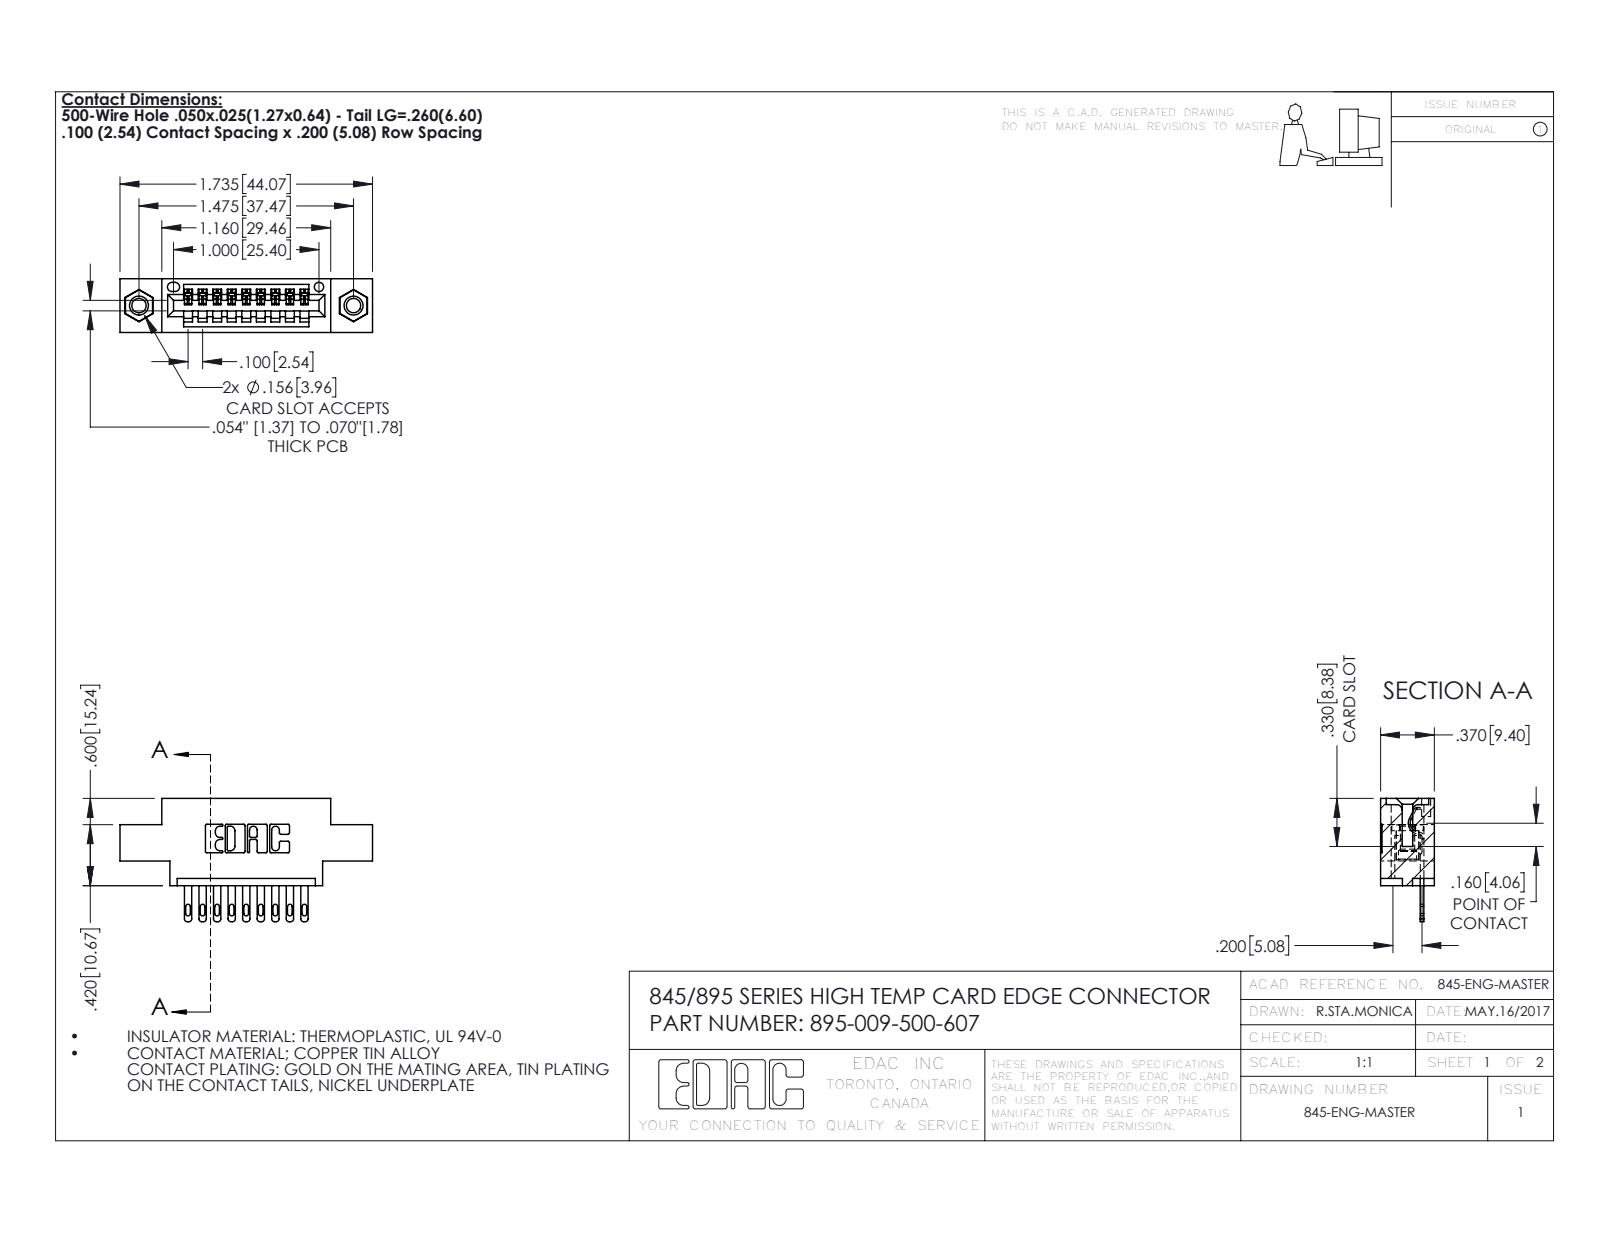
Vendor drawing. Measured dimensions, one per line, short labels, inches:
name: 895-009-500-607; 345-292-001_345-293-100; 845 Part_0.170 Offset - 0.156 Dia-TI; 345-250-001_345-250-005-103
written by: SolidWorks 2020 (CONFIG_CONTROL_DESIGN)
unit: in
bodies: 12 solids, 676 faces (422 planar, 238 cylindrical, 16 other)
size: 1.735 × 0.847 × 0.37
volume: 0.232 in³; area: 7.398 in²
holes: 2× ⌀0.098, 2× ⌀0.125, 2× ⌀0.156, 1× ⌀0.064
bosses: 2× ⌀0.155
rounds: 22× R0.01, 18× R0.006, 18× R0.016, 18× R0.02, 6× R0.007, 6× R0.031, 3× R0.026, 2× R0.031
face distances: 0.37, 0.2, 0.072, 0.298, 0.098, 0.272, 0.025, 0.1, 0.3, 0.6
hole spacings: 0.27, 1.244, 1.475
